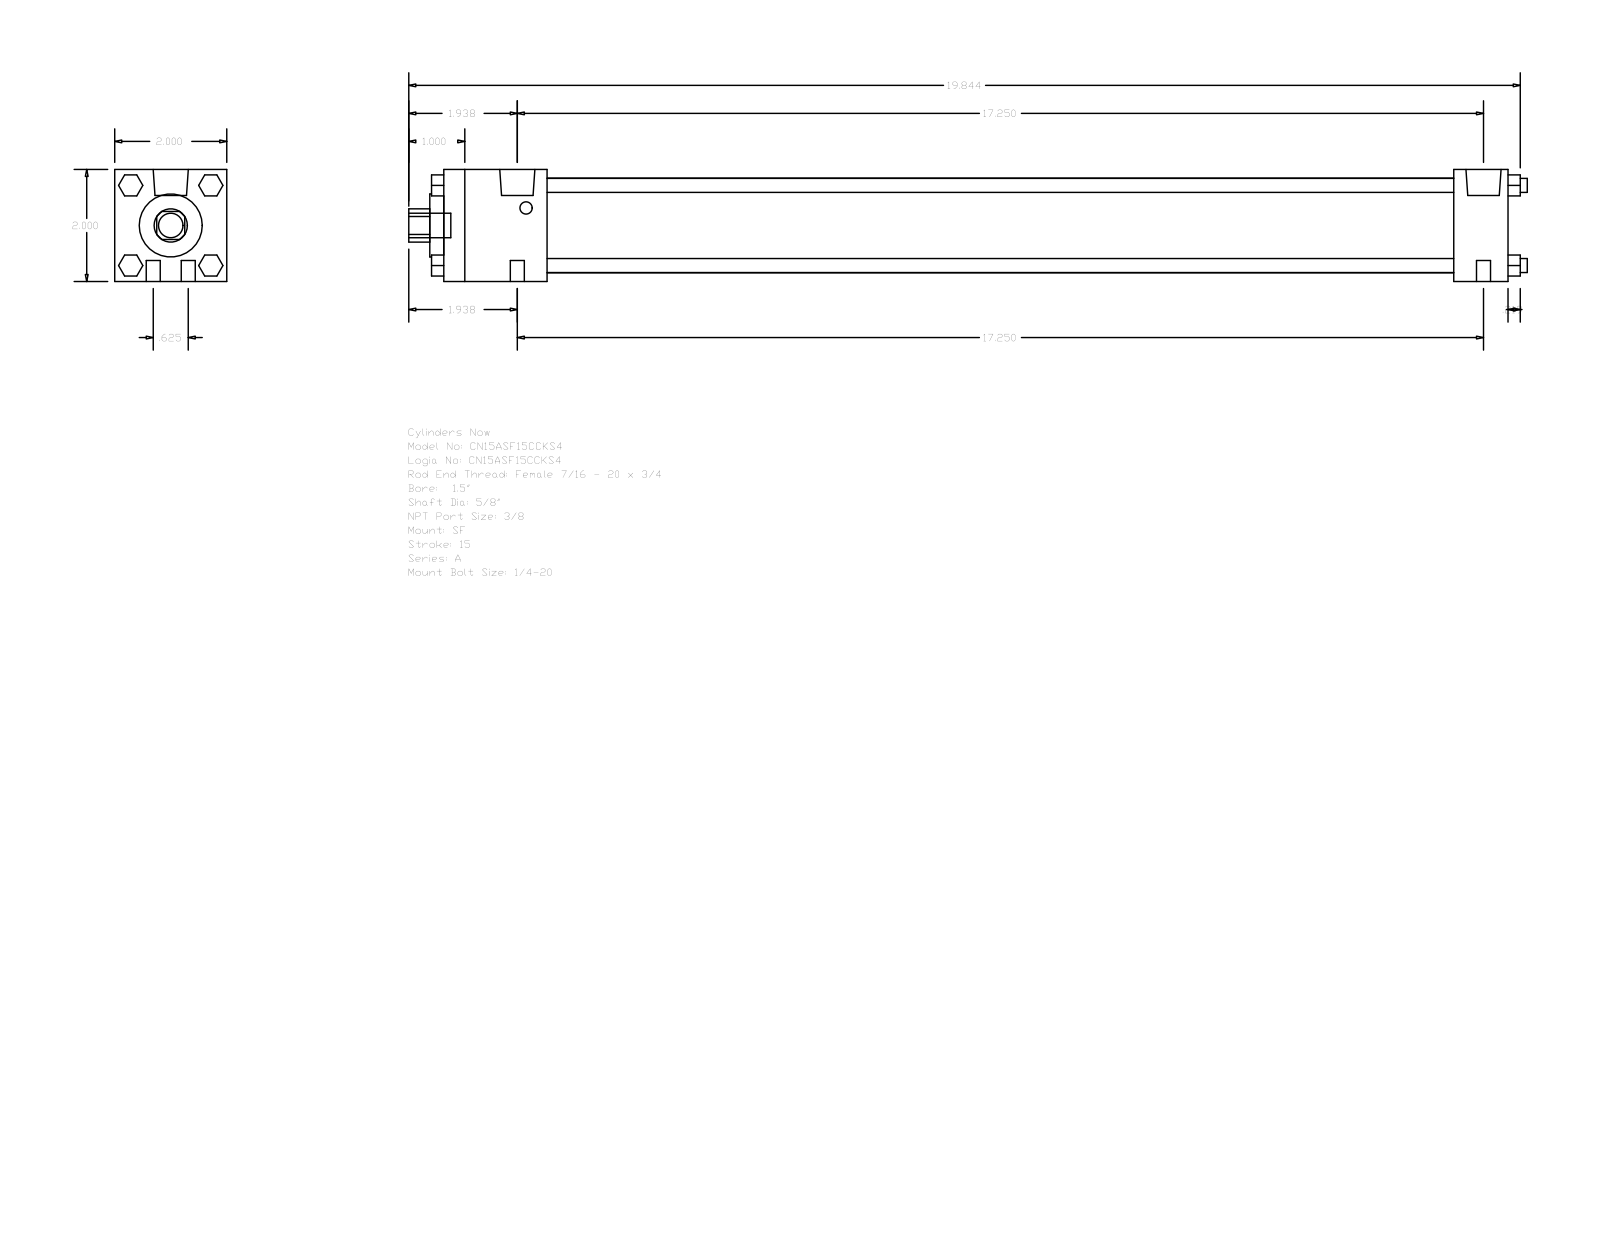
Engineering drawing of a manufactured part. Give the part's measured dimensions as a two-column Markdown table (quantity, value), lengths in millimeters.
| quantity | value |
| --- | --- |
| part name | A_SF__0150_0.625 |
| STEP written by | GSSL Pune (CONFIG_CONTROL_DESIGN) |
| units | millimeters |
| bodies | 0 solids, 124 faces (94 planar, 30 cylindrical, 0 other) |
| overall size | 507.21 × 50.8 × 50.8 |
| round holes (diameter × count) | 15.88 × 1, 28.57 × 1, 42.93 × 1 |
| round bosses / shafts (diameter × count) | 6.35 × 8, 15.93 × 2, 5.56 × 2, 11.11 × 1 |
| partial cylindrical surfaces (radius × count) | 7.54 × 1 |
| main face-to-face distances | 50.8, 482.6, 46.83, 457.99, 411.16, 435.77, 24.61, 9.52, 6.35, 53.18 |
